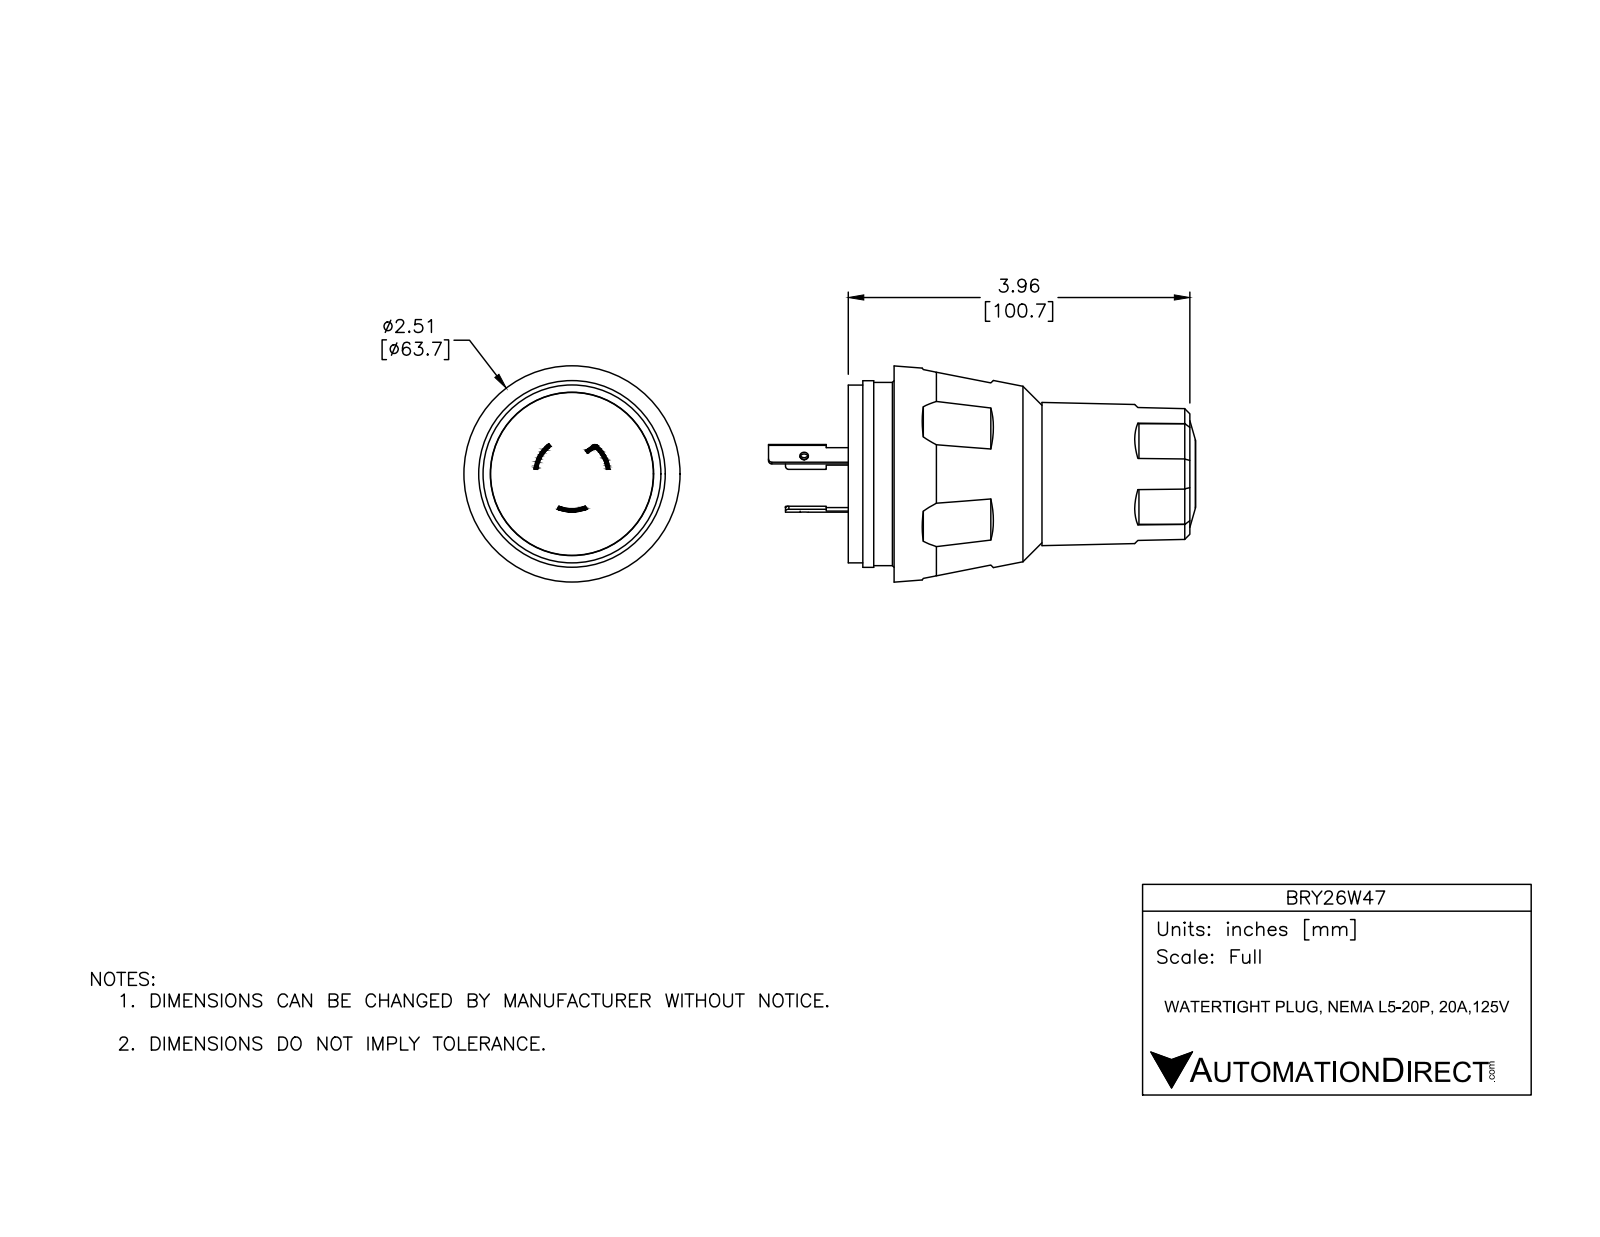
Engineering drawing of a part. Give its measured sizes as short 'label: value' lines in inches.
name: BRY26W47
written by: SolidWorks 2016 (AUTOMOTIVE_DESIGN)
unit: in
bodies: 7 solids, 167 faces (100 planar, 44 cylindrical, 23 other)
size: 4.956 × 2.508 × 2.508
volume: 11.44 in³; area: 57.86 in²
holes: 3× ⌀0.098, 1× ⌀0.689, 1× ⌀1.894
bosses: 1× ⌀2.165, 1× ⌀2.126, 1× ⌀2.063, 1× ⌀1.89, 1× ⌀1.24
rounds: 8× R0.039, 1× R0.384, 1× R0.404, 1× R0.443, 1× R0.463
face distances: 0.276, 0.256, 0.531, 2.74, 2.996, 3.272, 0.614, 3.354, 3.61, 3.886
